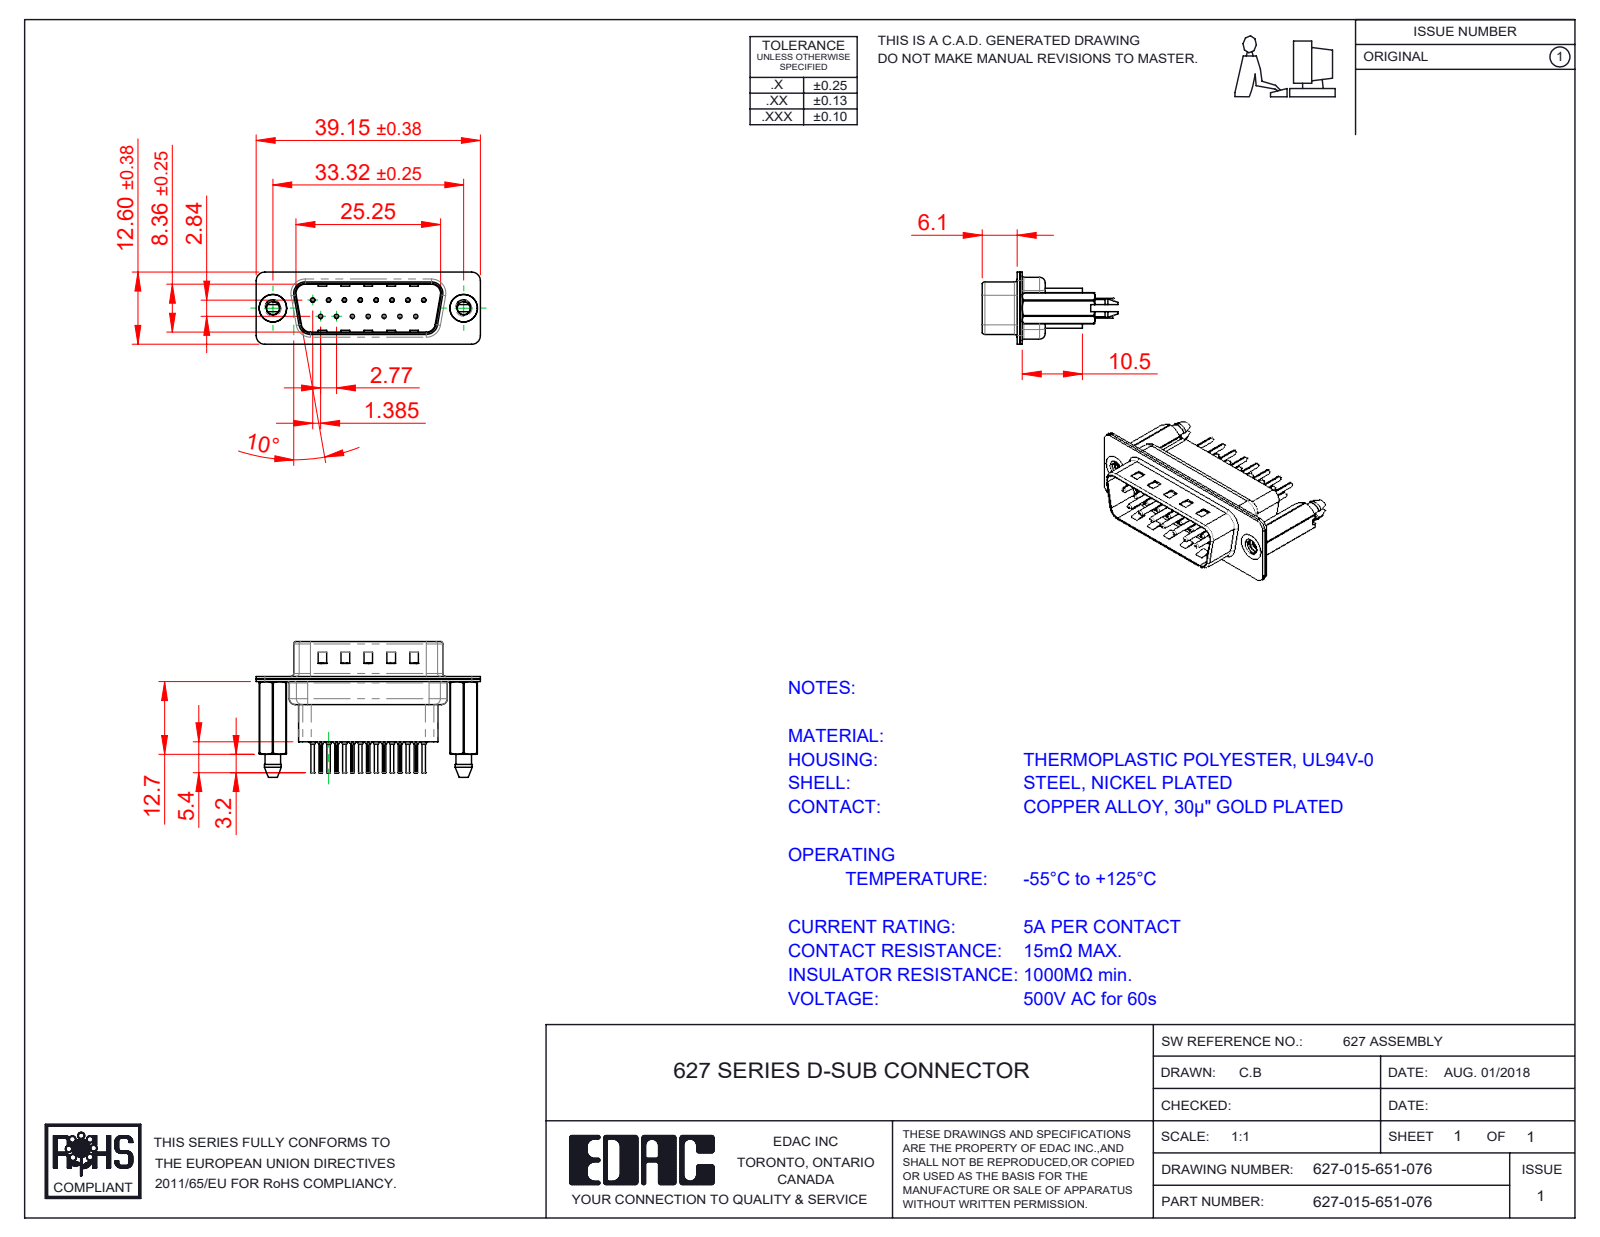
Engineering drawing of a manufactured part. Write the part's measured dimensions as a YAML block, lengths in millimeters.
part_name: "627 Housing_15 HP; 627 Shell Front_15 Contacts; 627 Contact Row 2_41; 627 4-40 Threaded Boardlock_HP51 (+3 more)"
step_written_by: "SolidWorks 2020 (CONFIG_CONTROL_DESIGN)"
units: millimeters
bodies: {solids: 20, faces: 1918, planar: 531, cylindrical: 754, other: 633}
overall_size: [39.15, 23.6, 12.6]
volume: 2858
surface_area: 7369
round_holes:
  - {diameter: 0.2, count: 15}
  - {diameter: 0.35, count: 15}
  - {diameter: 1.1, count: 15}
  - {diameter: 1.6, count: 15}
  - {diameter: 2.26, count: 2}
  - {diameter: 4, count: 2}
  - {diameter: 4.8, count: 2}
round_bosses_or_shafts:
  - {diameter: 2, count: 15}
  - {diameter: 1.5, count: 15}
  - {diameter: 0.75, count: 15}
  - {diameter: 0.6, count: 15}
  - {diameter: 4.9, count: 2}
partial_cylinders:
  - {radius: 0.1, count: 30}
  - {radius: 1.5, count: 18}
  - {radius: 2, count: 12}
  - {radius: 1.6, count: 10}
  - {radius: 0.5, count: 8}
  - {radius: 0.25, count: 4}
  - {radius: 0.6, count: 4}
  - {radius: 0.65, count: 4}
face_to_face_distances: [0.4, 0.45, 0.9, 0.82, 9.58, 1.5, 0.68, 7.68, 4.76, 1.4]
hole_center_spacings: [3.16, 2.77, 5.54, 8.31, 11.08, 5.03, 5.04, 7.48]
